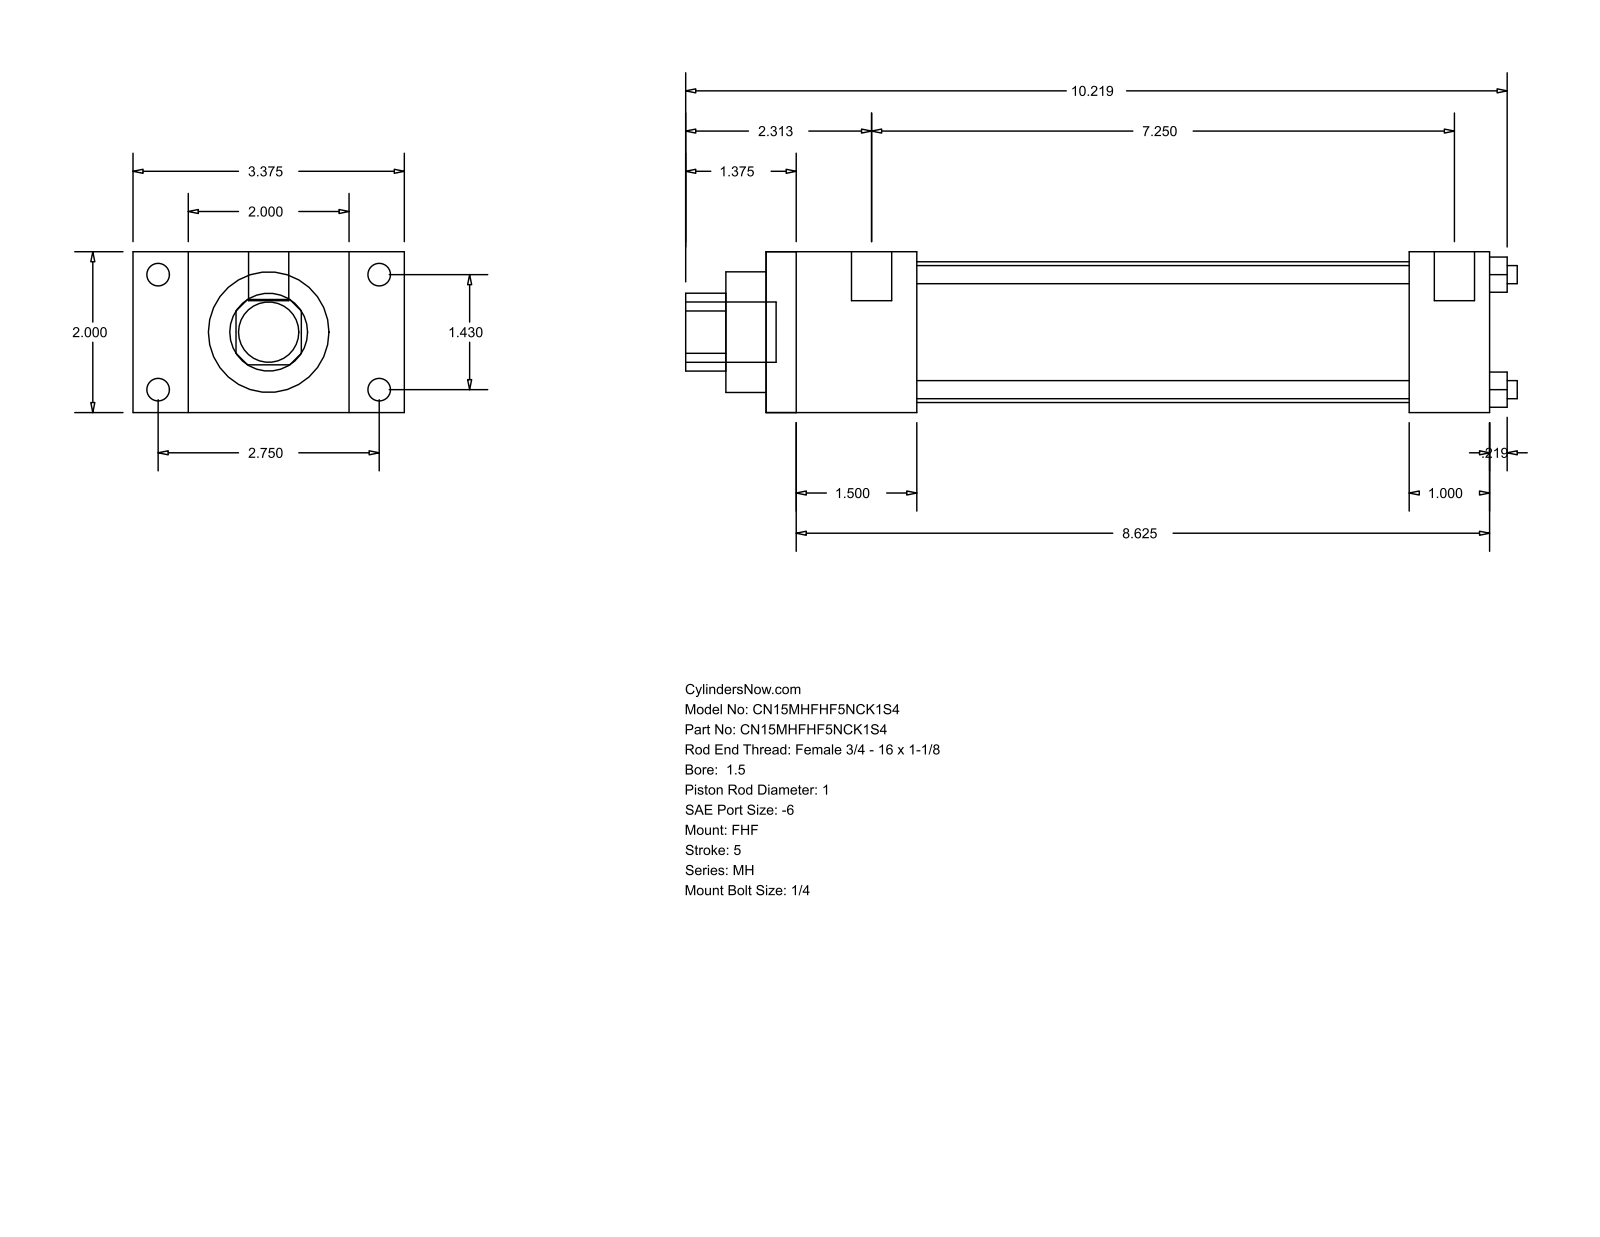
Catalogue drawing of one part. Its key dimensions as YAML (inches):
part_name: "MH_FHF__0150_1"
step_written_by: "GSSL Pune (CONFIG_CONTROL_DESIGN)"
units: inches
bodies: {solids: 0, faces: 88, planar: 60, cylindrical: 28, other: 0}
overall_size: [10.344, 3.375, 2]
round_holes:
  - {diameter: 0.225, count: 4}
  - {diameter: 1, count: 1}
  - {diameter: 1.5, count: 1}
  - {diameter: 1.75, count: 1}
round_bosses_or_shafts:
  - {diameter: 0.281, count: 4}
  - {diameter: 0.219, count: 4}
  - {diameter: 0.5, count: 2}
  - {diameter: 0.75, count: 1}
partial_cylinders:
  - {radius: 0.484, count: 1}
face_to_face_distances: [2, 0.687, 2.687, 1.875, 3.375, 9, 7.125, 1, 8, 6.125]
hole_center_spacings: [1.011, 1.43, 2.022]
